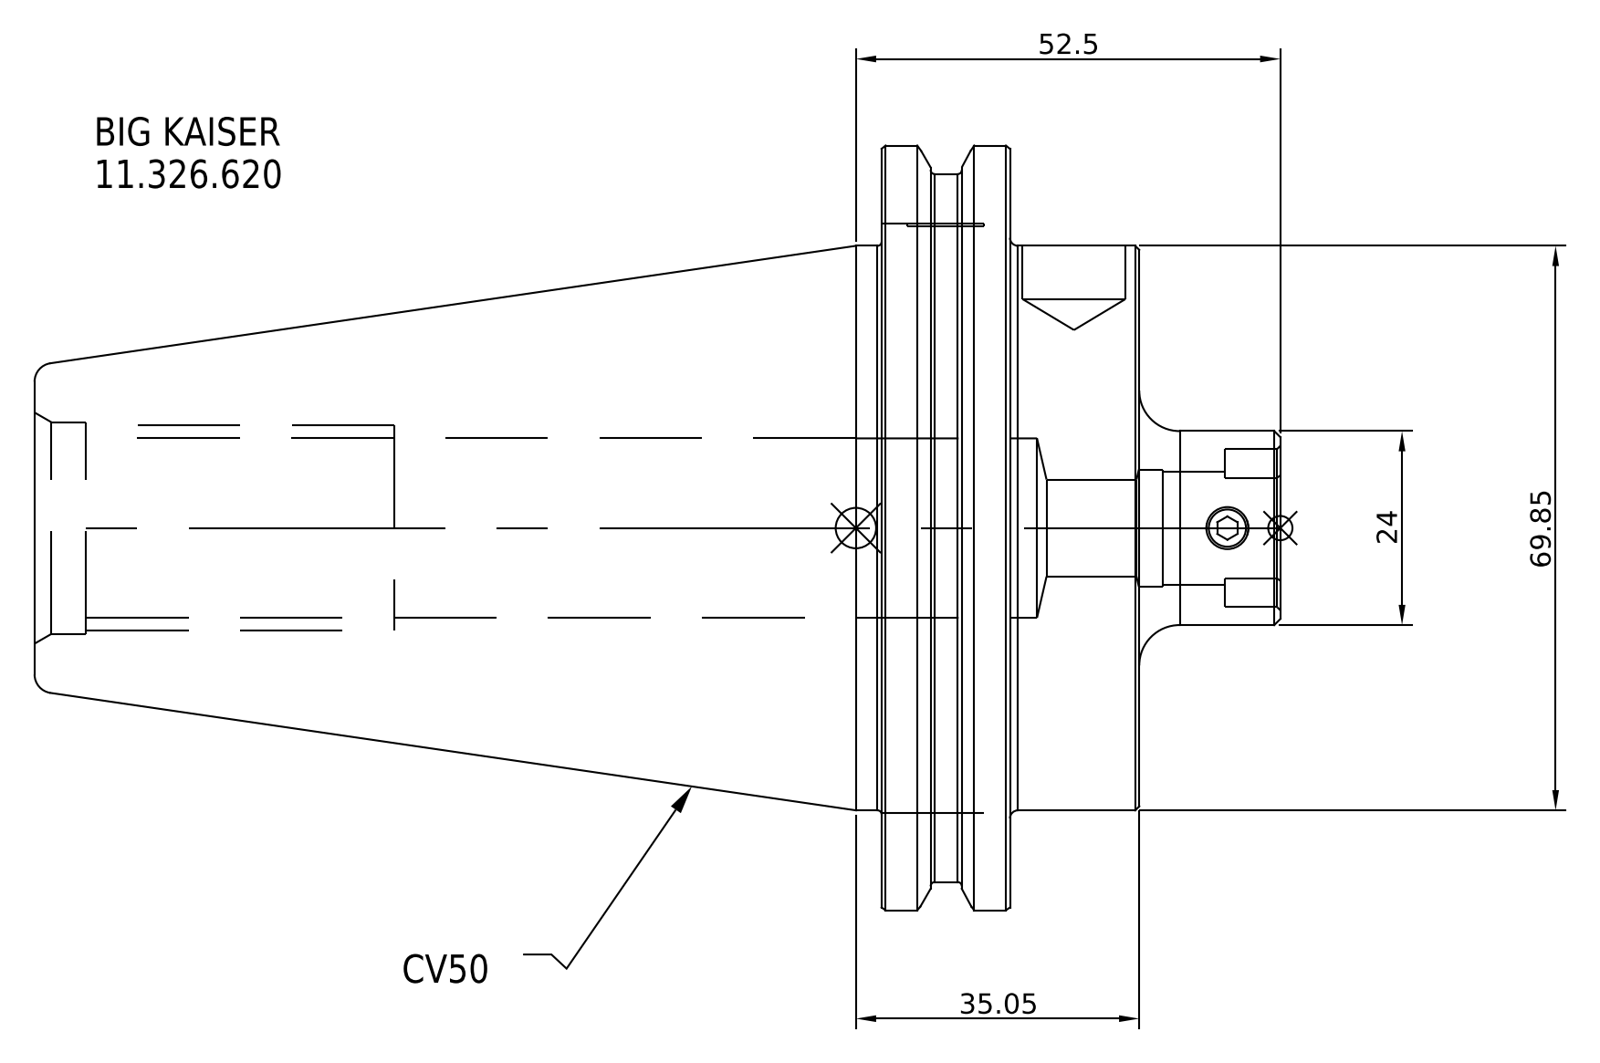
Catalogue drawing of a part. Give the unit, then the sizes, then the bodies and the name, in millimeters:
Units: millimetres
Overall size (bounding box): 154.1 × 98.43 × 98.43
Round bosses / shafts (diameter × count): ⌀98.43 ×1, ⌀91.29 ×1, ⌀69.85 ×1, ⌀24 ×1
Main face-to-face distances: 17.55, 15.95, 33.5, 136.6, 120.65, 103.1, 17.5, 33.45, 51, 154.1
Volume: 450 397 mm³ · Surface area: 42 293 mm²
Bodies: 1 solid, 16 faces (7 planar, 6 cylindrical, 3 other)
Part name (STEP PRODUCT): 11.326.620
STEP written by: SolidWorks 2021 (CONFIG_CONTROL_DESIGN)
